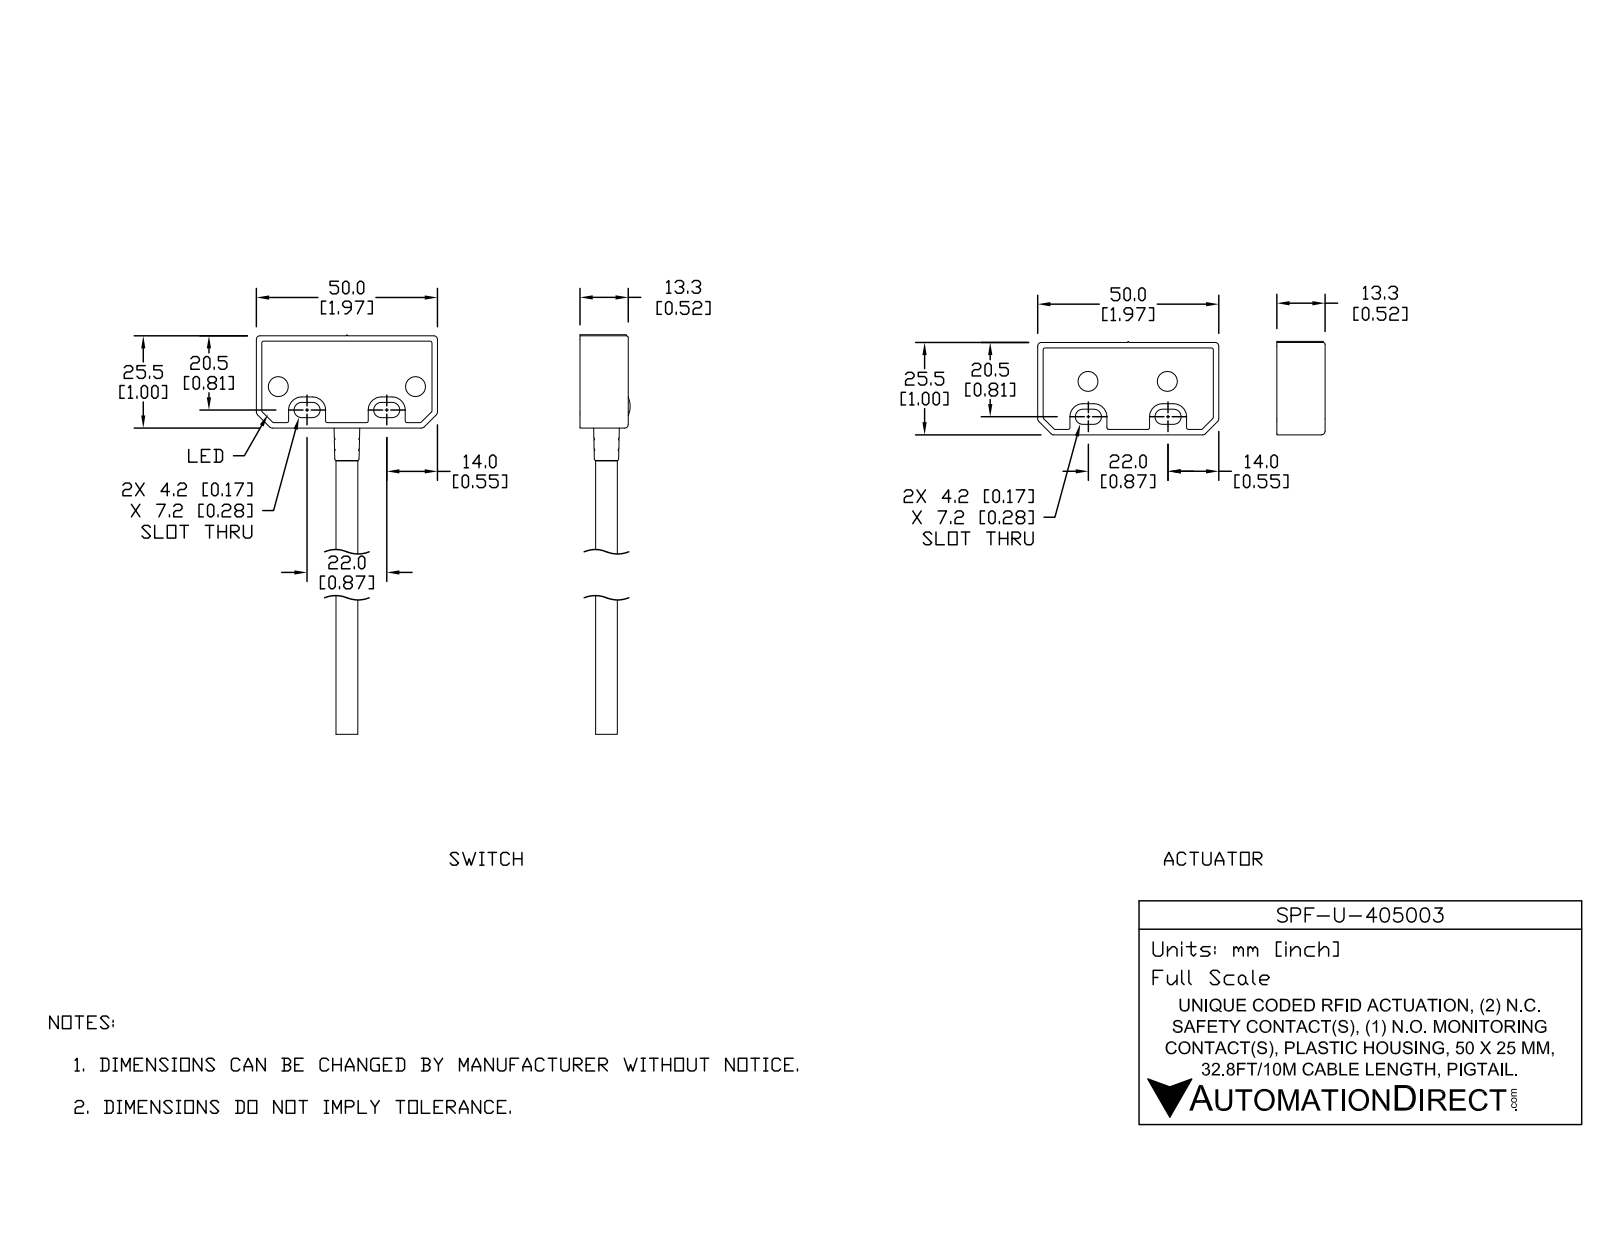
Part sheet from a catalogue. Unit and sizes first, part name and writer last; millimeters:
Units: millimetres
Overall size (bounding box): 205.5 × 50 × 13.8
Round holes (diameter × count): ⌀5 ×4, ⌀3 ×1, ⌀4.4 ×1, ⌀5.4 ×1, ⌀5.9 ×1, ⌀7 ×1
Round bosses / shafts (diameter × count): ⌀2 ×4, ⌀4.9 ×2, ⌀0.8 ×2, ⌀8.6 ×1, ⌀7.6 ×1, ⌀7.1 ×1, ⌀6 ×1, ⌀5.3 ×1
Partial cylindrical surfaces — rounded edges, fillets, slot ends (radius × count): R0.5 ×132, R1 ×36, R2 ×8, R2.1 ×8, R3.6 ×8, R4.6 ×8, R0.3 ×6, R3.6 ×4
Main face-to-face distances: 1.5, 11.6, 10.1, 1.2, 11.3, 12.8, 26.5, 2.5, 24, 48.5
Hole centre spacings: 5.6, 21.9, 27, 27.1, 32.6, 37.9, 39.4, 39.6
Volume: 18 110 mm³ · Surface area: 23 430 mm²
Bodies: 12 solids, 1147 faces (475 planar, 358 cylindrical, 314 other)
Part name (STEP PRODUCT): SPF-U-405003_1; SPF-U-405003; SPF-U-405003_2
STEP written by: SolidWorks 2017 (AUTOMOTIVE_DESIGN)
